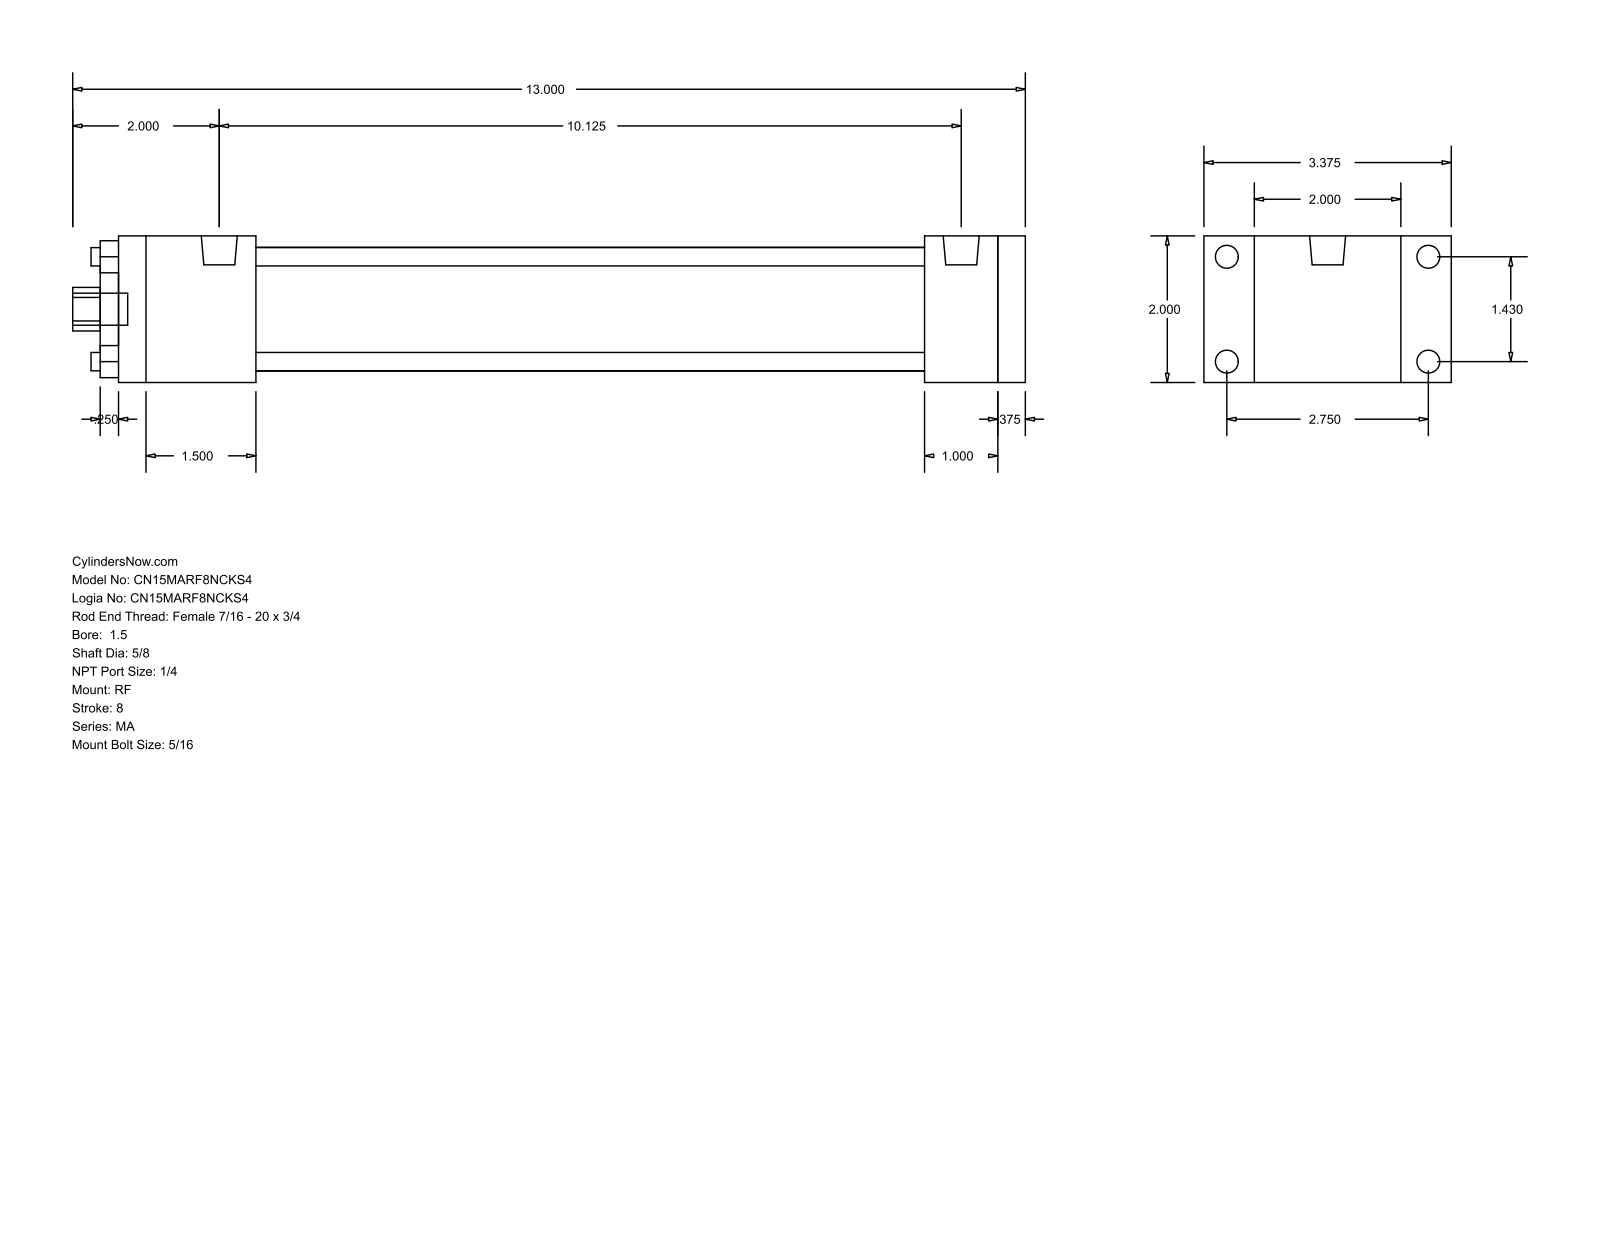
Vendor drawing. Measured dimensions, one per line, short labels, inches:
name: MA_RF__0150_0.625
written by: GSSL Pune (CONFIG_CONTROL_DESIGN)
unit: in
bodies: 0 solids, 92 faces (64 planar, 28 cylindrical, 0 other)
size: 13 × 3.375 × 2
holes: 4× ⌀0.25, 1× ⌀0.625, 1× ⌀1.125, 1× ⌀1.69
bosses: 8× ⌀0.313, 2× ⌀0.492, 1× ⌀0.437
rounds: 1× R0.297
face distances: 2, 0.375, 12, 12.375, 11, 1, 1.375, 1.875, 9.125, 10.125
hole spacings: 1.011, 1.43, 2.022
